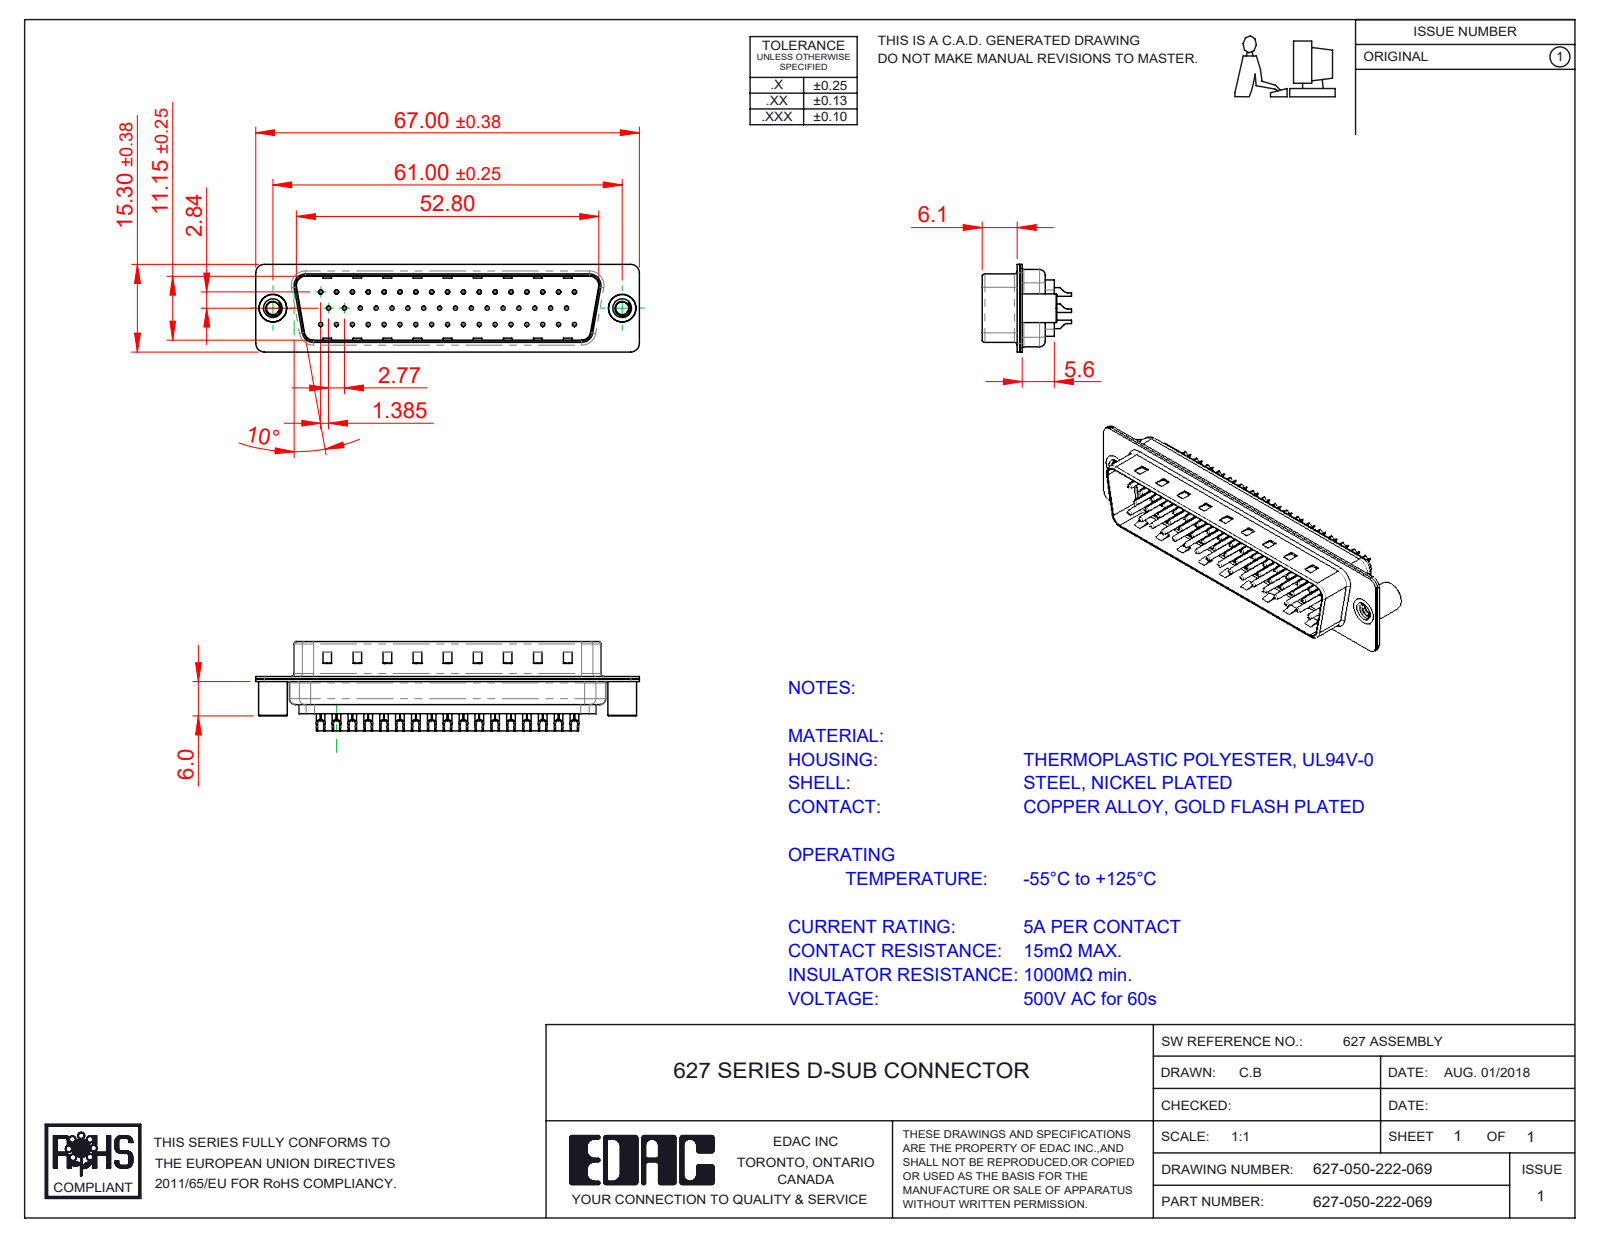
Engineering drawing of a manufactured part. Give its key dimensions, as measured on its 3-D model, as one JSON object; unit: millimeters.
{"part_name": "627 Shell Rear_50 Contacts; 627 Housing_50 LP; 627 Shell Front_50 Contacts; 627-050-222-069 (+4 more)", "step_written_by": "SolidWorks 2020 (CONFIG_CONTROL_DESIGN)", "units": "millimeters", "bodies": {"solids": 55, "faces": 3634, "planar": 903, "cylindrical": 1611, "other": 1120}, "overall_size": [67, 15.6, 15.3], "volume_mm3": 4548, "surface_area_mm2": 12964, "round_holes": [[1.6, 58], [0.35, 50], [1.1, 50], [0.75, 8], [2, 8], [2.26, 2], [4, 2], [4.8, 2]], "round_bosses_or_shafts": [[2, 50], [1.5, 50], [0.75, 50], [5, 2], [4.9, 2]], "partial_cylinders_radius": [[1.5, 16], [2, 12], [0.5, 8], [1.6, 8], [1, 7], [0.25, 4], [0.6, 4], [0.65, 4]], "face_to_face_distances": [0.4, 0.45, 11.55, 0.9, 6.05, 6.5, 0.78, 1.95, 0.77, 12.33], "hole_center_spacings": [2.77, 3.16, 5.54, 8.31, 11.08, 13.85, 16.62, 19.39]}
